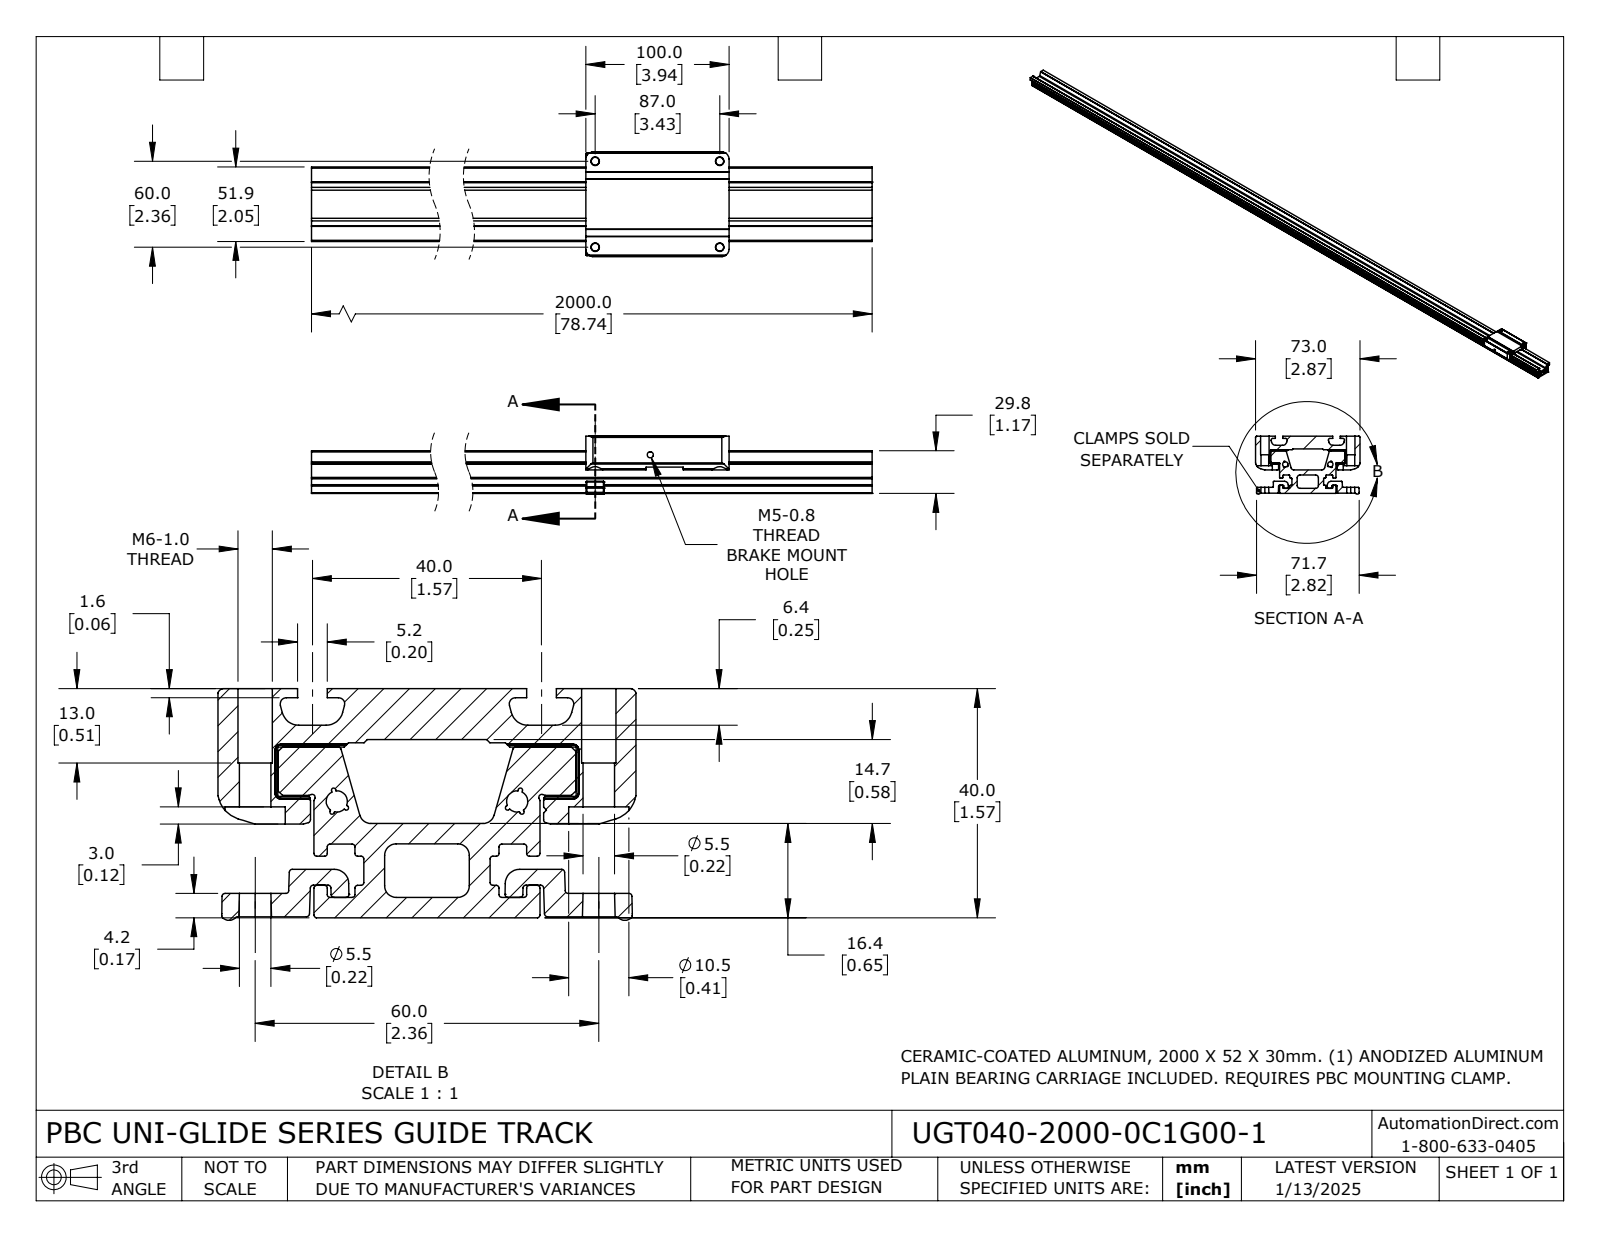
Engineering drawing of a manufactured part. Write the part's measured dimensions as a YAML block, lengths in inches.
part_name: "UGT040-2000-0C1G00-1_CARRIAGE; UGT040-2000-0C1G00-1; UGT040-2000-0C1G00-1_RAIL"
step_written_by: "SolidWorks 2023 (CONFIG_CONTROL_DESIGN)"
units: inches
bodies: {solids: 10, faces: 445, planar: 248, cylindrical: 178, other: 19}
overall_size: [78.74, 2.874, 1.575]
volume: 83.19
surface_area: 1005
round_holes:
  - {diameter: 0.098, count: 4}
  - {diameter: 0.118, count: 4}
  - {diameter: 0.217, count: 4}
  - {diameter: 0.236, count: 4}
  - {diameter: 0.413, count: 4}
  - {diameter: 0.146, count: 2}
  - {diameter: 0.165, count: 1}
partial_cylinders:
  - {radius: 0.019, count: 26}
  - {radius: 0.039, count: 8}
  - {radius: 0.094, count: 8}
  - {radius: 0.015, count: 6}
  - {radius: 0.197, count: 6}
  - {radius: 0.02, count: 4}
  - {radius: 0.035, count: 4}
  - {radius: 0.043, count: 4}
face_to_face_distances: [0.14, 0.507, 1.173, 0.648, 0.526, 1.033, 1.553, 0.246, 1.799, 0.367]
hole_center_spacings: [0.591, 1.221, 1.615, 1.811, 2.205, 2.283, 2.359, 2.362]
